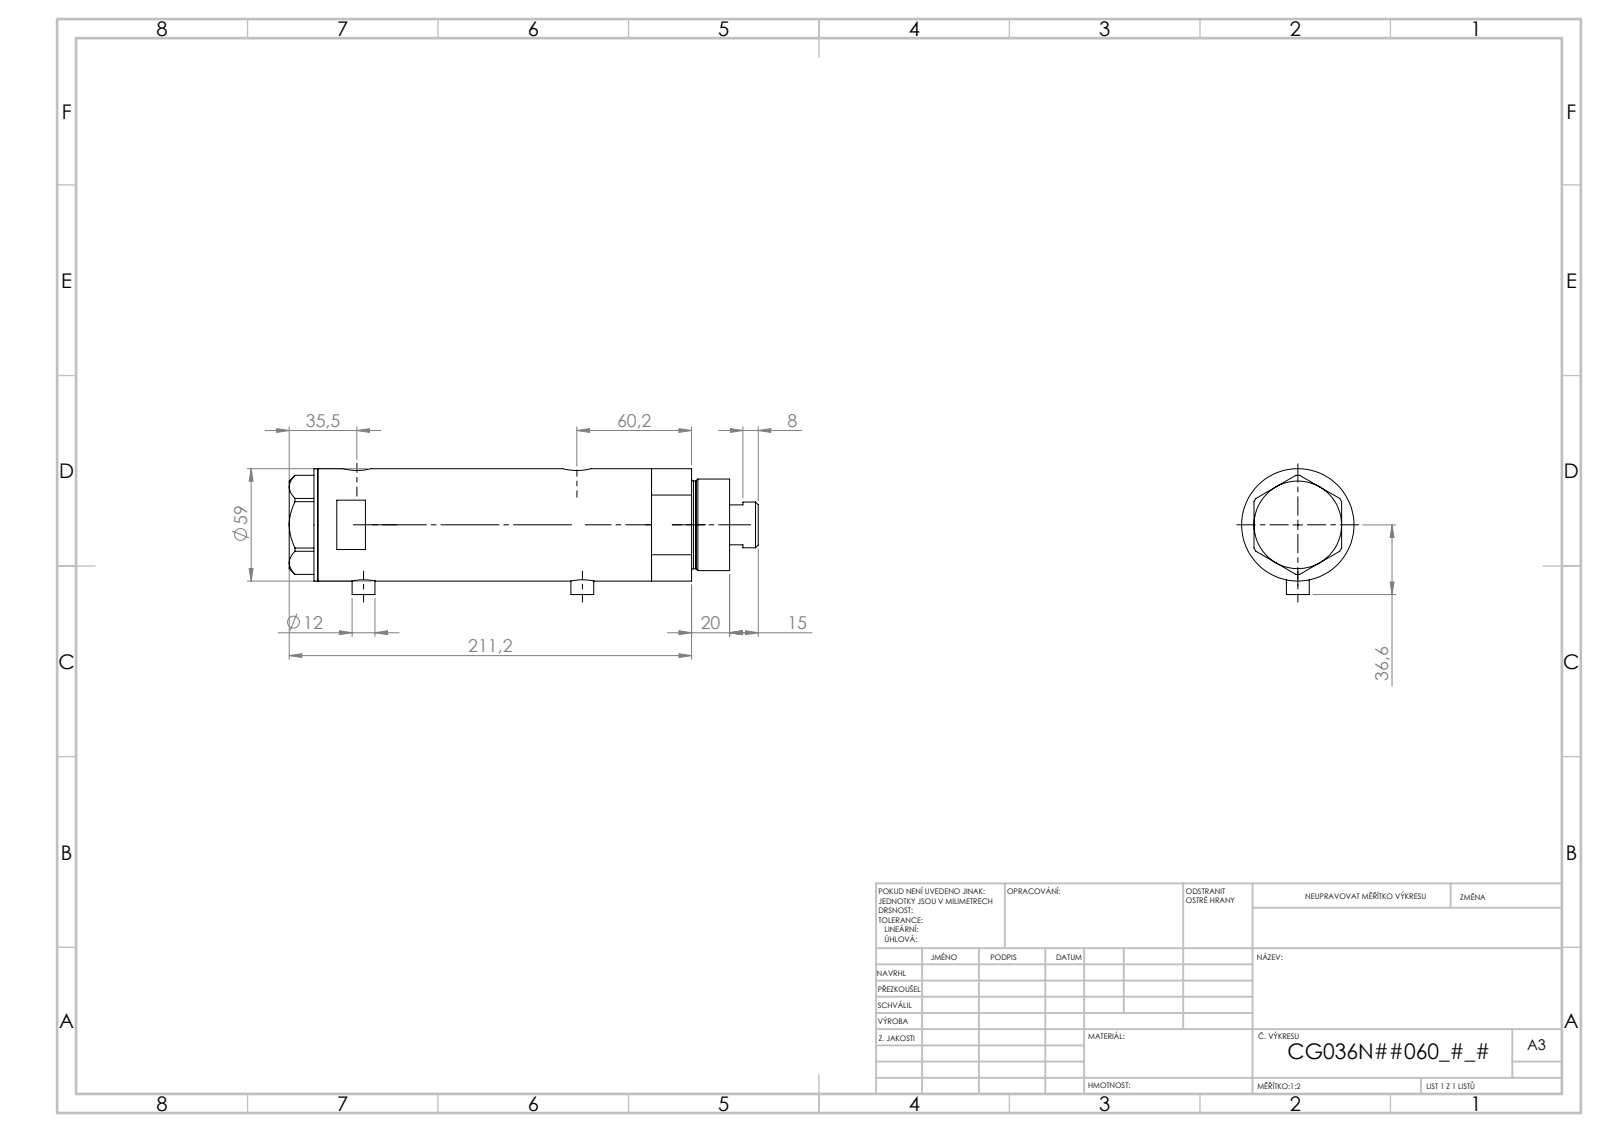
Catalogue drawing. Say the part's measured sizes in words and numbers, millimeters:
The part is named "V270CG_BACK; V270CG_VC; V270CG_FRONT; V270CG_MIDDLE". Its 3-D file was written by "SolidWorks 2019 (CONFIG_CONTROL_DESIGN)". It is 4 solids with 126 faces: 53 planar, 53 cylindrical and 20 other. Overall it measures 223.42 by 60.1 by 59 millimeters. Its volume is 503 560 cubic millimeters and its surface area 104 512 square millimeters. Round holes: 2 of diameter 5, 2 of diameter 9.73, 2 of diameter 12.5, 2 of diameter 15, 1 of diameter 8.5, 1 of diameter 25, 1 of diameter 26.5, 1 of diameter 36, 1 of diameter 40, 1 of diameter 52. Round bosses or shafts: 2 of diameter 12, 1 of diameter 59, 1 of diameter 48, 1 of diameter 46, 1 of diameter 24. The main face-to-face distances are 117.34, 23.5, 93.84, 15, 38.5, 132.34, 208.42, 193.42, 169.92, 76.08. The hole center spacings are 2.9, 3.5, 92.15, 95.05, 95.65, 98.55, 2.89, 2.91.
